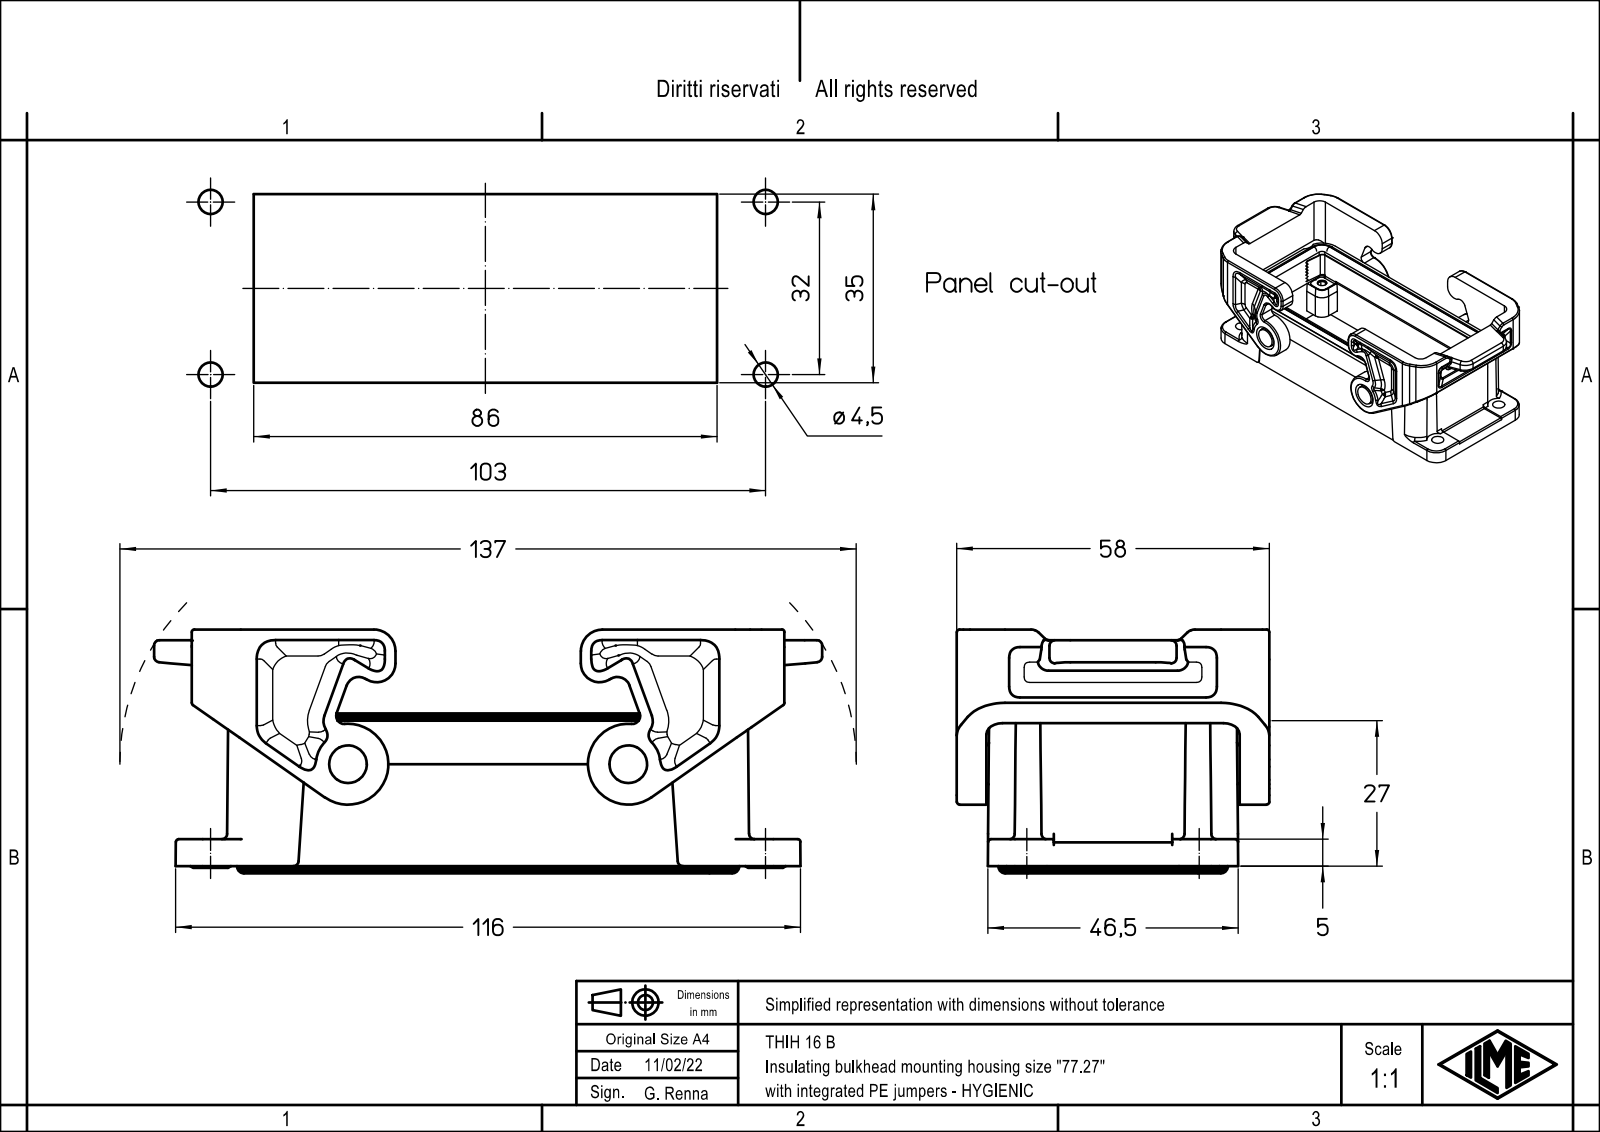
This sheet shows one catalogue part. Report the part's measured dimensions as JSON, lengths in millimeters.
{"part_name": "53622; THIH_16", "step_written_by": "Creo Elements/Direct Modeling 20.1B 02-Apr-2019 (C) Parametric Technology GmbH (AUTOMOTIVE_DESIGN)", "units": "millimeters", "bodies": {"solids": 1, "faces": 923, "planar": 472, "cylindrical": 265, "other": 186}, "overall_size": [124, 58, 45.25], "volume_mm3": 70539, "surface_area_mm2": 41342, "round_holes": [[2.5, 4], [3.5, 4], [4.5, 4], [7.2, 2]], "round_bosses_or_shafts": [[4.8, 4], [7, 2]], "partial_cylinders_radius": [[1, 29], [1.3, 20], [1.5, 18], [2, 16], [2.7, 12], [3, 12], [5.5, 12], [5, 8]], "face_to_face_distances": [5.9, 41.1, 35.2, 40.4, 5.5, 45.9, 11.4, 46.6, 52.5, 6.6], "hole_center_spacings": [12.99, 32.14, 90.28, 94.95, 27, 32, 77.5, 82.07]}
